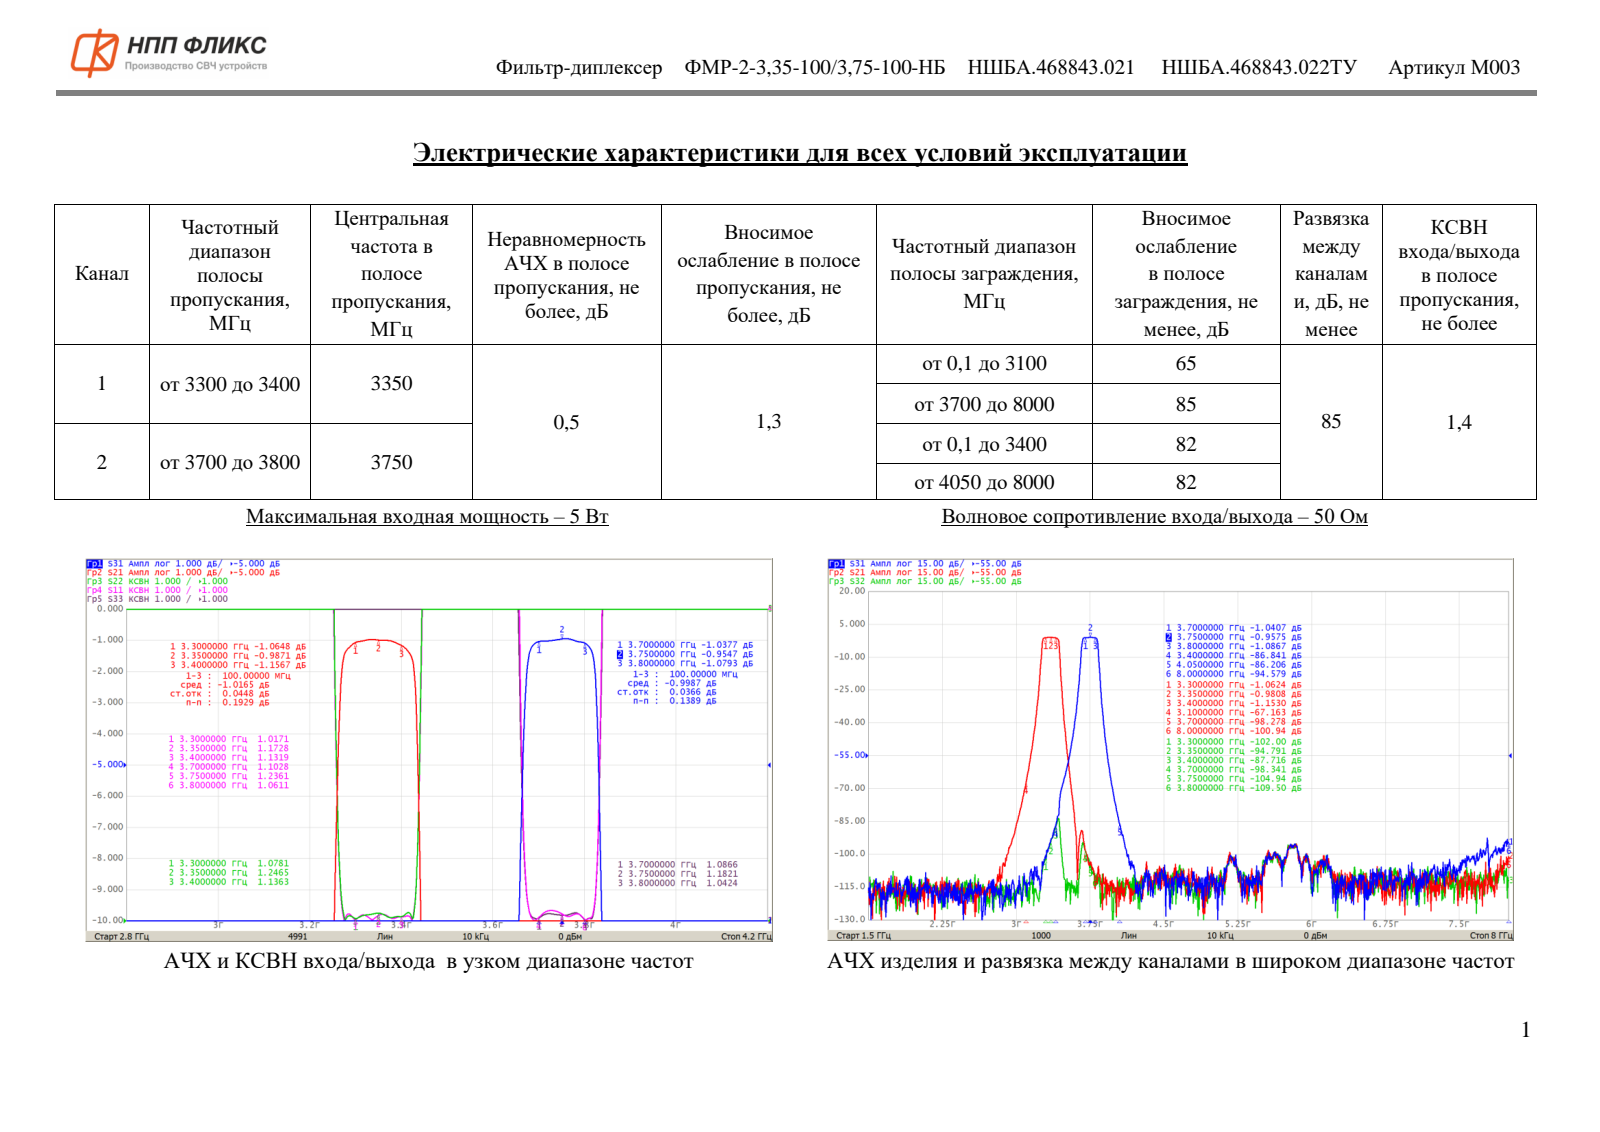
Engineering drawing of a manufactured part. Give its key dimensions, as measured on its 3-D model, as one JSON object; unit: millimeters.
{"part_name": "НШБА.468843.021_Диплексер ФМР-2-3,35-100(3,75-100-НБ", "step_written_by": "ASCON Math Kernel (CONFIG_CONTROL_DESIGN)", "units": "millimeters", "bodies": {"solids": 55, "faces": 2851, "planar": 2063, "cylindrical": 380, "other": 408}, "overall_size": [81.4, 61, 22], "volume_mm3": 57534, "surface_area_mm2": 24225, "round_holes": [[2.9, 41], [2.05, 28], [2.6, 28], [5.1, 28], [1.6, 25], [2.5, 4], [0.6, 3], [4.6, 3], [4.8, 3], [5.2, 3], [6.4, 3], [7, 3]], "round_bosses_or_shafts": [[2.5, 41], [5, 31], [3.8, 28], [2, 25], [4.7, 13], [6, 3]], "partial_cylinders_radius": [[2, 20], [3, 4], [0.7, 3], [5, 2], [0.35, 1], [1.05, 1], [1.23, 1]], "face_to_face_distances": [17, 3, 20, 40, 2, 1, 70, 0.6, 18, 1.6], "hole_center_spacings": [25, 20, 5, 20.62, 10, 22.36, 15, 28.28]}
